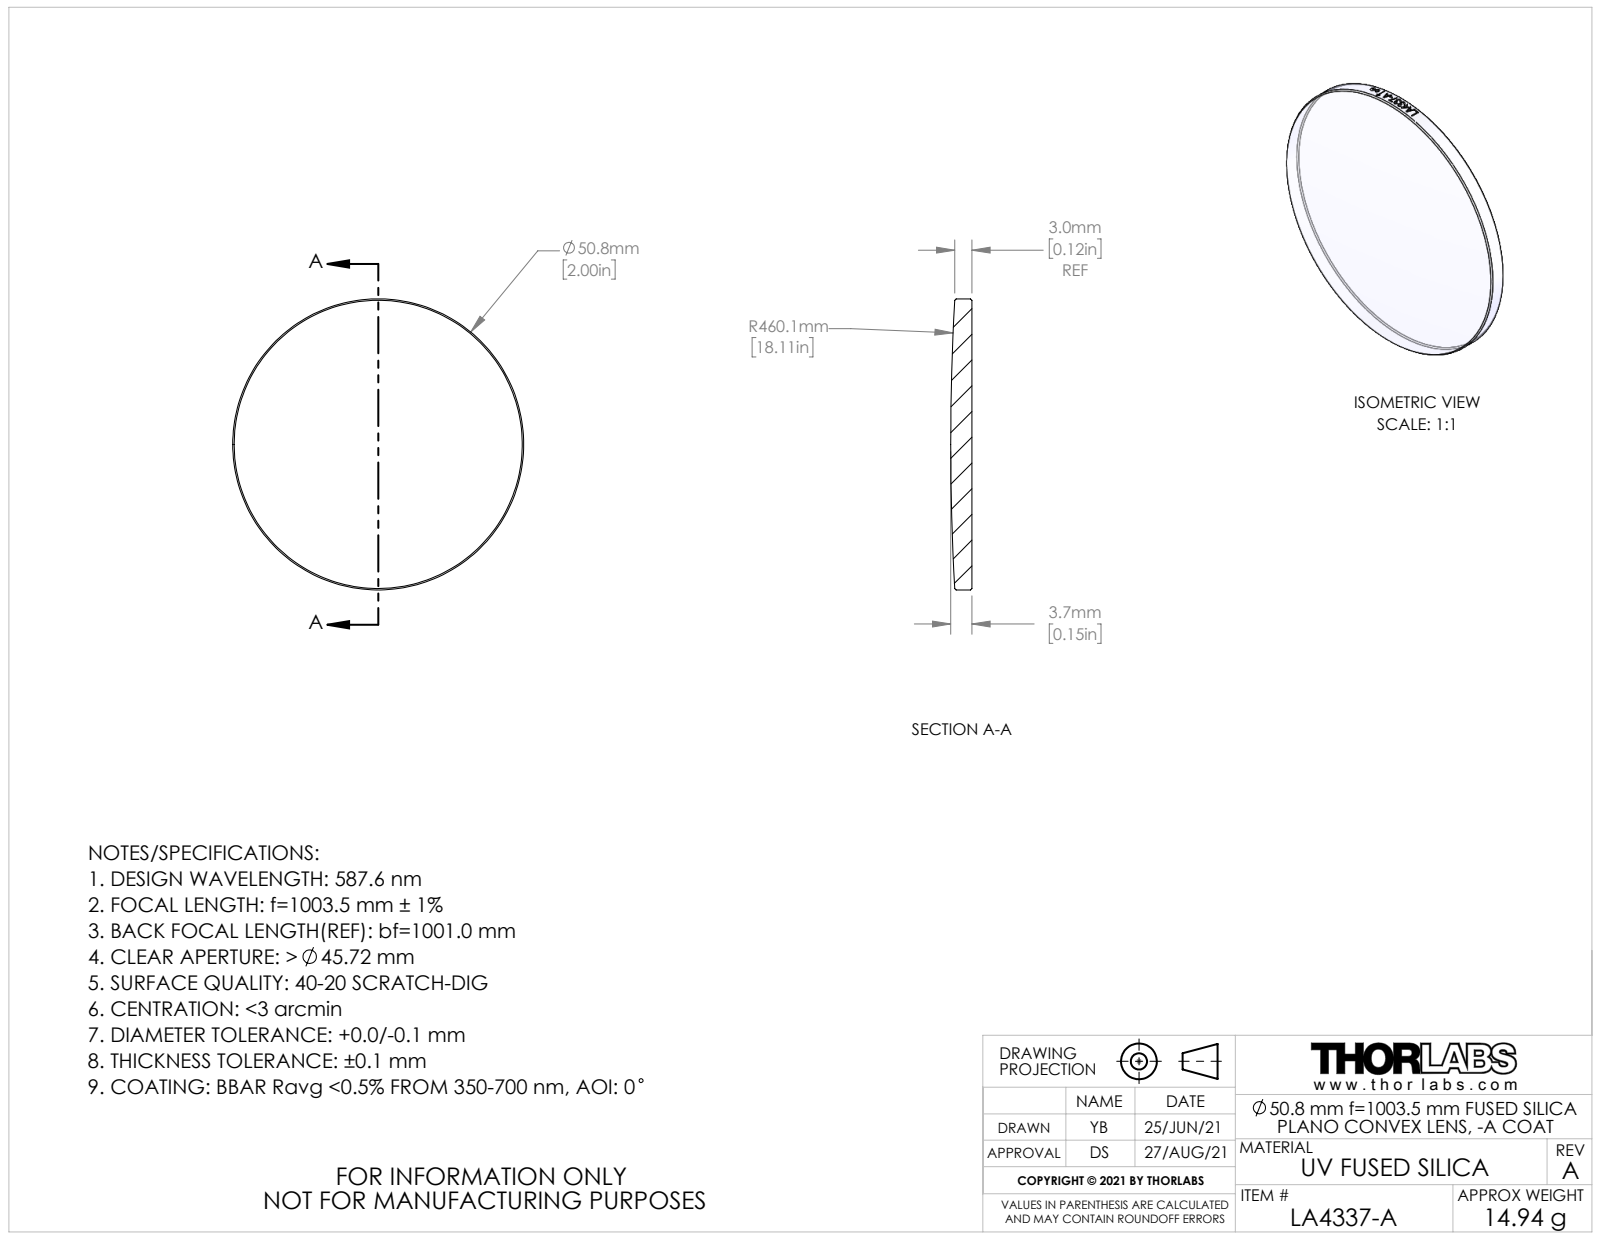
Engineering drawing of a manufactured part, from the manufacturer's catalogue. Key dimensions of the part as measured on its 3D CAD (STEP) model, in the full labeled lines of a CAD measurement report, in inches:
Part name (STEP PRODUCT): CTN017544-E0W; CTN017572
STEP written by: SolidWorks 2018 (AUTOMOTIVE_DESIGN)
Units: inches
Bodies: 1 solid, 24 faces (1 planar, 17 cylindrical, 6 other)
Overall size (bounding box): 2 × 2 × 0.146
Volume: 0.414 in³ · Surface area: 6.958 in²
Round bosses / shafts (diameter × count): ⌀2 ×1
